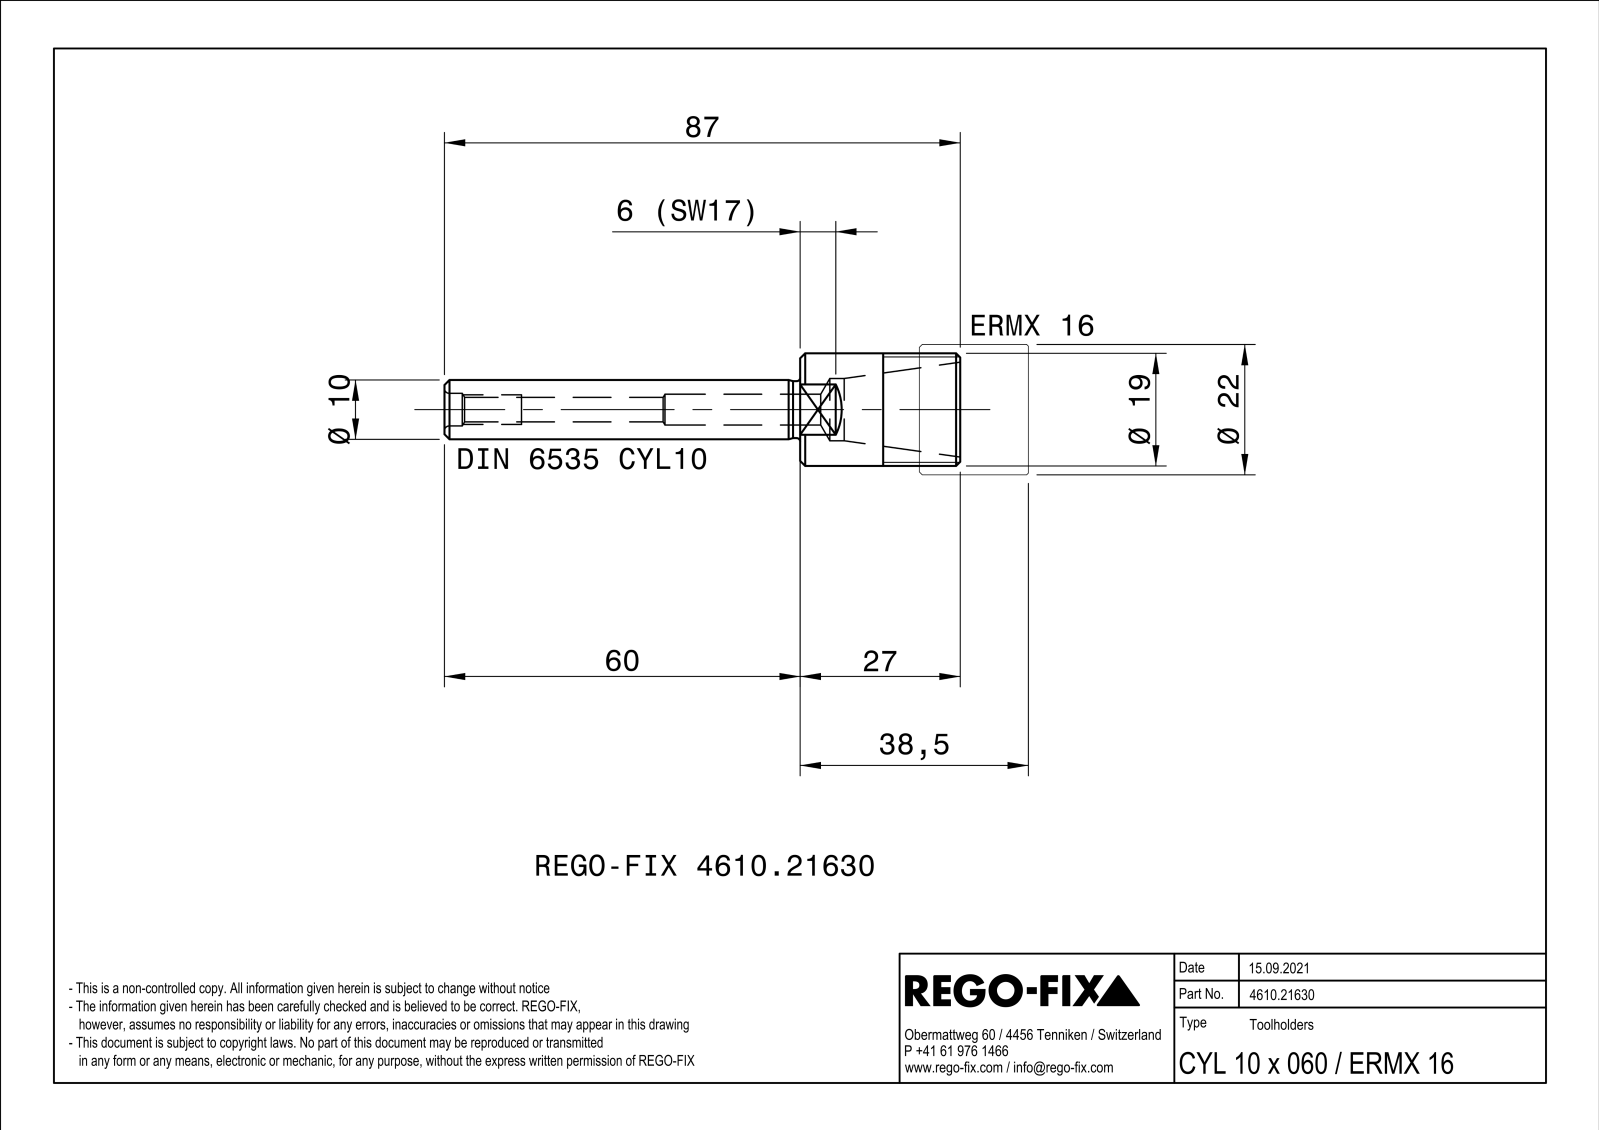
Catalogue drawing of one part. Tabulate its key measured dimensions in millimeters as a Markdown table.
| quantity | value |
| --- | --- |
| part name | NOCUT |
| STEP written by | SIEMENS PLM Software Solid Edge ST10 (AUTOMOTIVE_DESIGN) |
| units | millimeters |
| bodies | 1 solid, 30 faces (9 planar, 9 cylindrical, 12 other) |
| overall size | 87 × 19 × 19 |
| volume | 8 120 mm³ |
| surface area | 5 657 mm² |
| round holes (diameter × count) | 4.13 × 1, 5.2 × 1, 5.5 × 1, 10.5 × 1 |
| round bosses / shafts (diameter × count) | 19 × 1, 10 × 1, 9.6 × 1 |
| main face-to-face distances | 17, 27, 3.53, 87, 60 |
